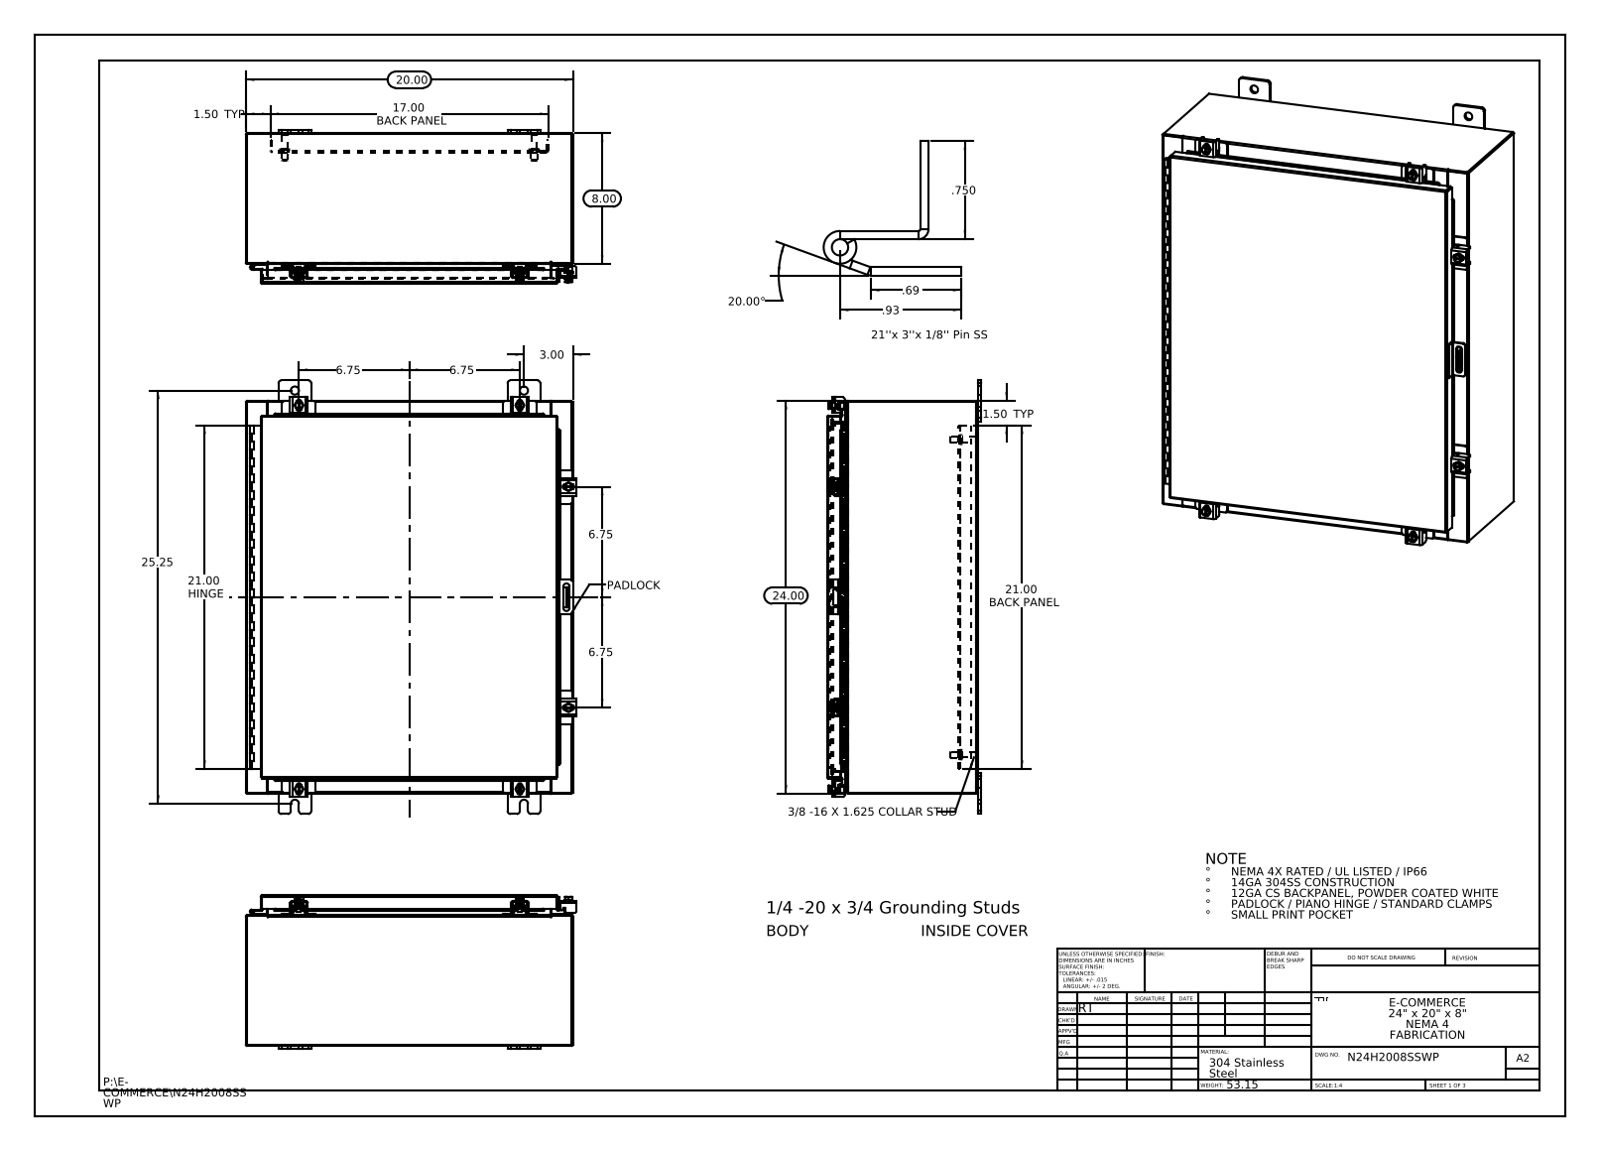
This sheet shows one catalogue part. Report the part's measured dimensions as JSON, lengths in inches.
{"part_name": "N24H2008SSWP Padlock Staple; N24H2008SSWP Backpanel; N24H2008SSWP Body; N24H2008SSWP Clamp Assembly (+8 more)", "step_written_by": "SolidWorks 2013 (CONFIG_CONTROL_DESIGN)", "units": "inches", "bodies": {"solids": 47, "faces": 1709, "planar": 908, "cylindrical": 705, "other": 96}, "overall_size": [26.5, 20.211, 9.389], "volume_in3": 187, "surface_area_in2": 4712, "round_holes": [[0.5, 8], [0.213, 6], [0.26, 6], [0.125, 2], [0.125, 1]], "round_bosses_or_shafts": [[0.25, 7], [0.5, 6], [0.399, 6], [0.625, 4], [0.375, 4], [0.33, 4]], "partial_cylinders_radius": [[0.06, 30], [0.013, 25], [0.19, 24], [0.088, 21], [0.12, 12], [0.141, 12], [0.125, 10], [0.05, 9]], "face_to_face_distances": [0.075, 9.126, 9.201, 9.051, 0.104, 19.925, 1, 1.075, 8.051, 8.126], "hole_center_spacings": [21.369, 25.739, 13.5, 0.431, 0.934, 1.858, 2.275, 2.276]}
